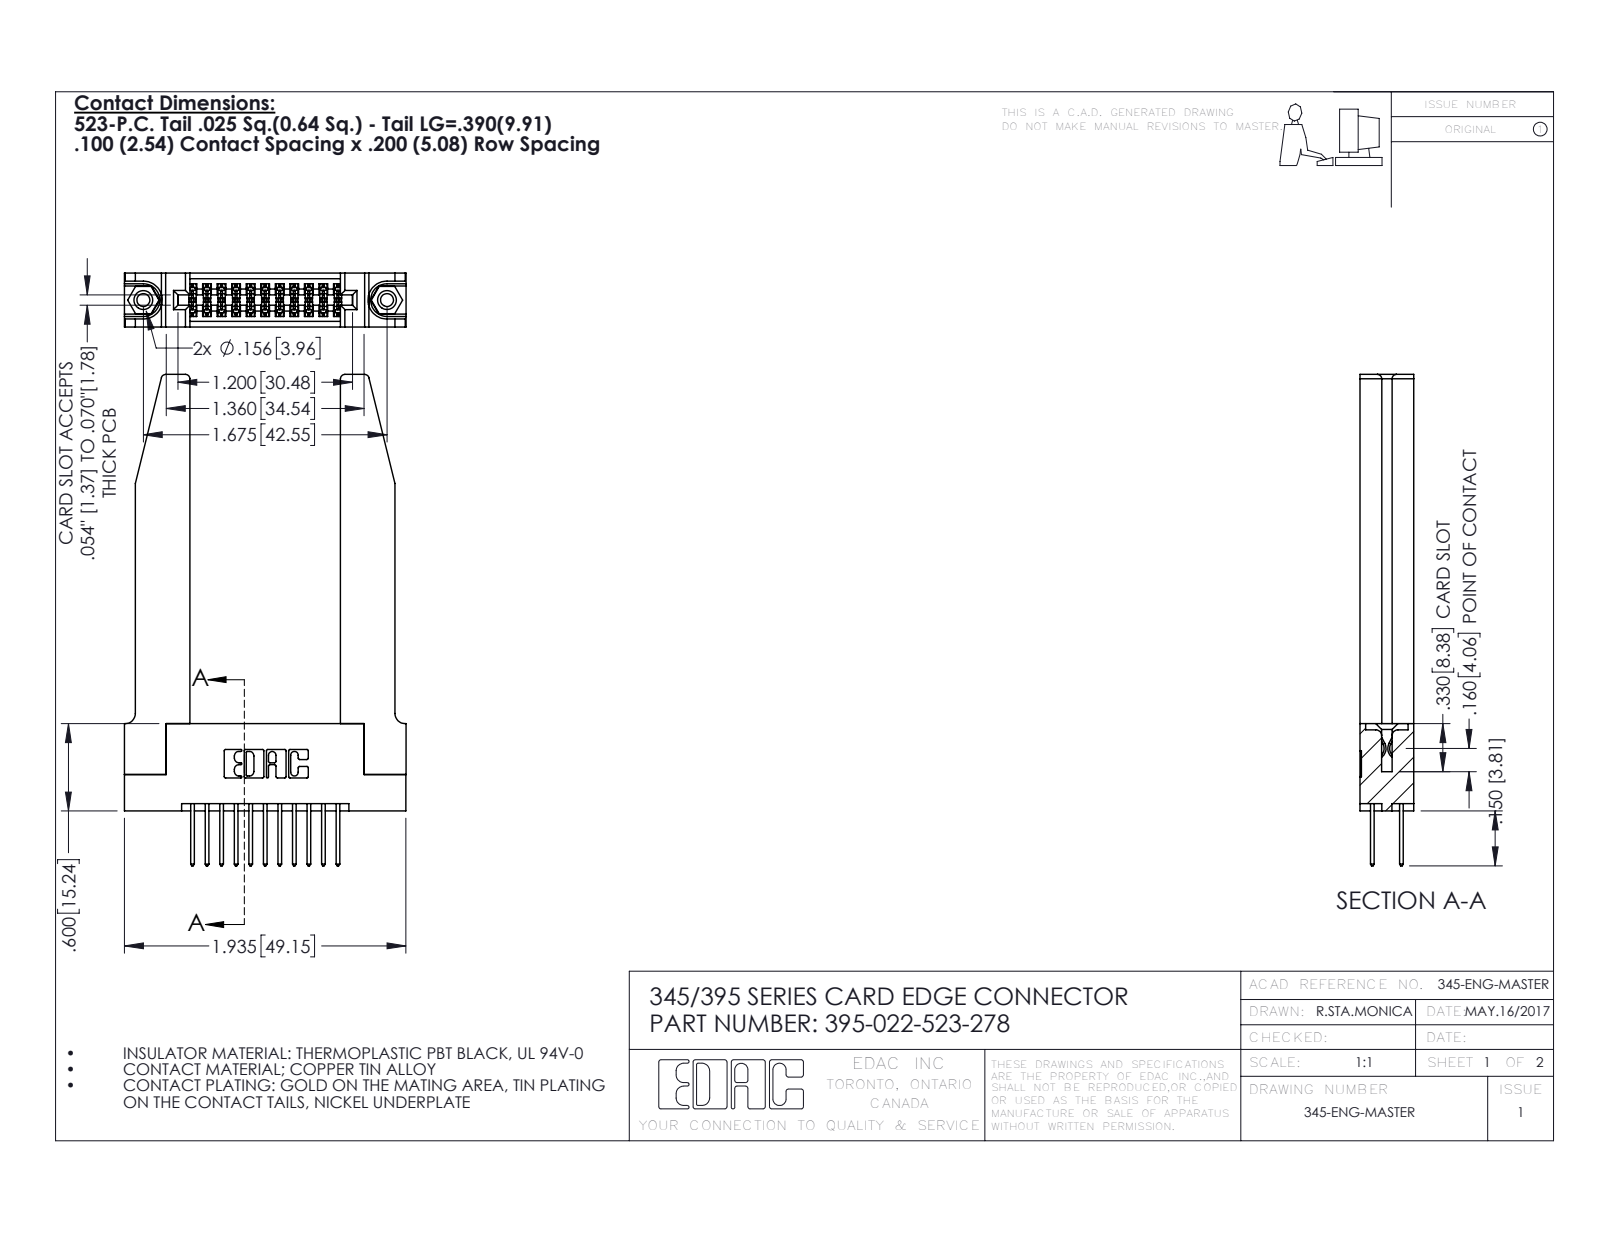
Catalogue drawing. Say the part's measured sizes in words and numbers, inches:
The part is named "345 Part_Flush Mounting Lugs - 0.156 Dia-TH; 345-250-001_345-250-001-102; 395-022-523-278; 345-292-001_345-293-123 (+1 more)". Its 3-D file was written by "SolidWorks 2016 (CONFIG_CONTROL_DESIGN)". It is 27 solids with 1460 faces: 948 planar, 460 cylindrical and 52 other. Overall it measures 3.377 by 1.936 by 0.37 inches. Its volume is 0.751 cubic inches and its surface area 20.37 square inches. Round holes: 2 of diameter 0.089, 2 of diameter 0.125, 2 of diameter 0.156, 1 of diameter 0.064. Round bosses or shafts: 2 of diameter 0.155. Partial cylindrical surfaces (rounded edges, fillets, slot ends): 33 of radius 0.006, 22 of radius 0.01, 22 of radius 0.01, 8 of radius 0.03, 6 of radius 0.007, 6 of radius 0.031, 3 of radius 0.026, 2 of radius 0.014. The main face-to-face distances are 0.37, 0.072, 0.298, 0.2, 0.148, 0.15, 0.077, 0.22, 0.098, 0.272. The hole center spacings are 0.27, 1.443, 1.675.
